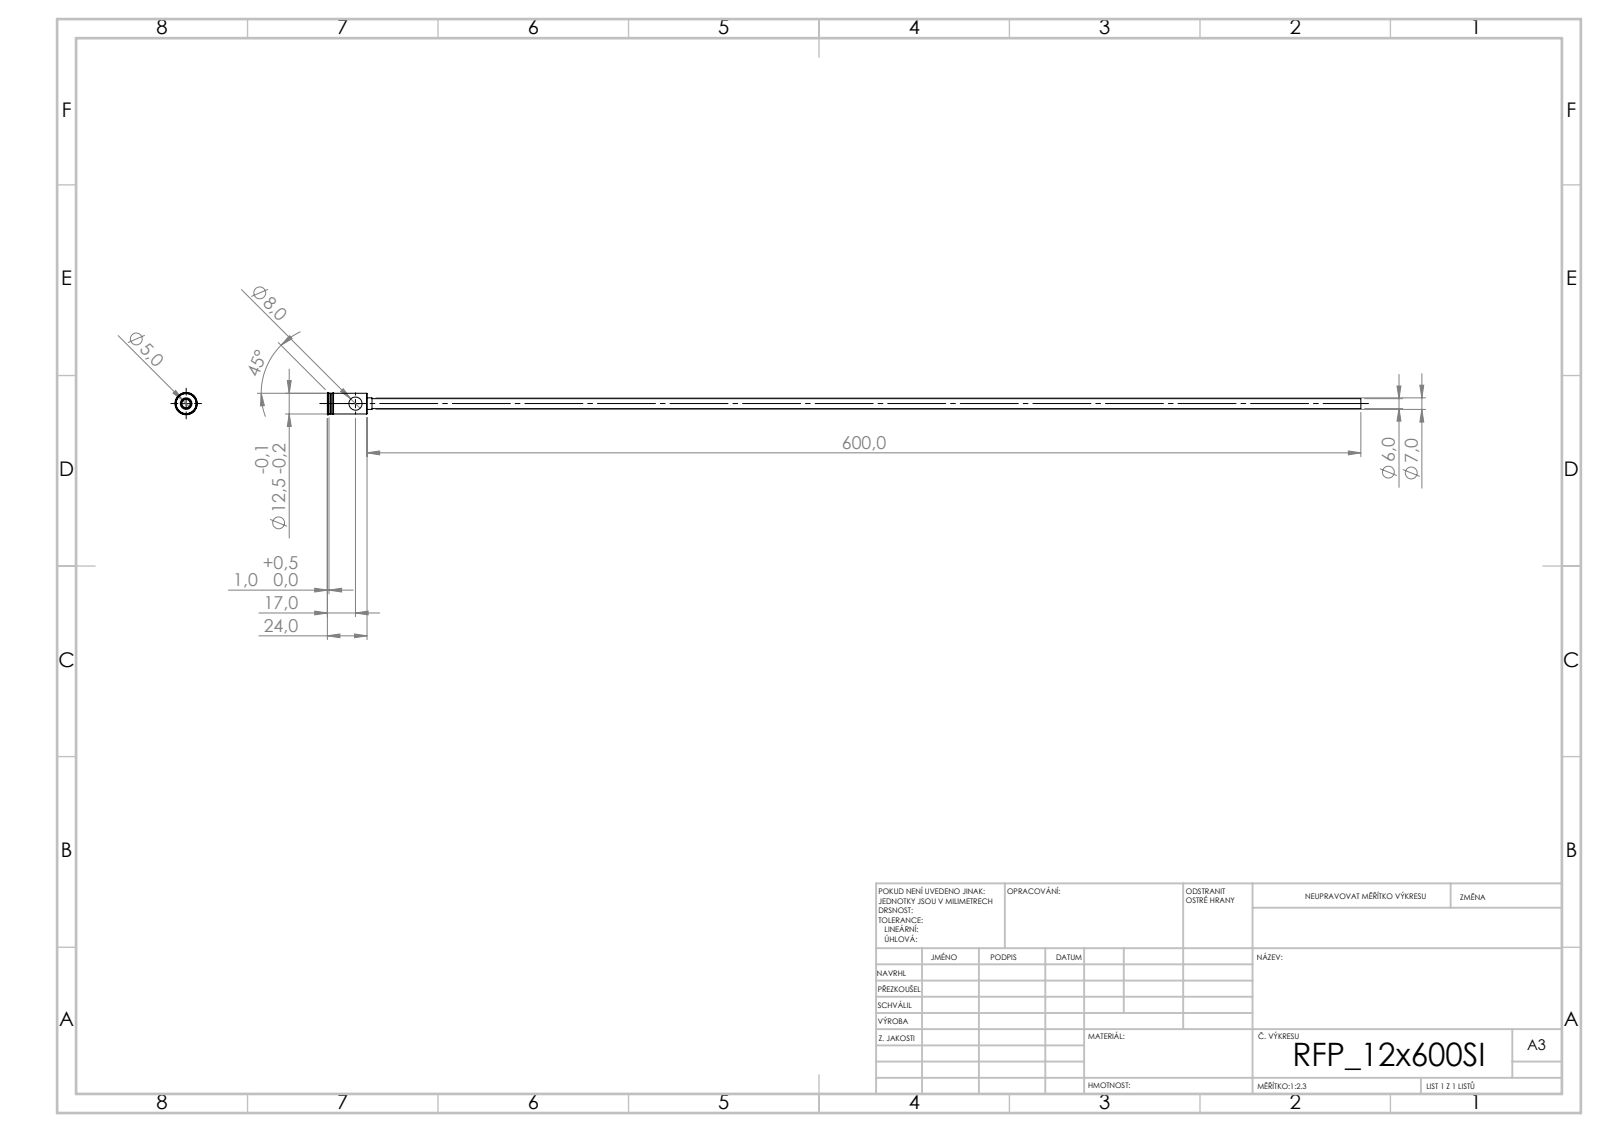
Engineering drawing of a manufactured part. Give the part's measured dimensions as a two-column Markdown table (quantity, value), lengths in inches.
| quantity | value |
| --- | --- |
| STEP written by | SolidWorks 2019 (CONFIG_CONTROL_DESIGN) |
| units | inches |
| bodies | 1 solid, 44 faces (20 planar, 16 cylindrical, 8 other) |
| overall size | 24.567 × 0.531 × 0.531 |
| volume | 0.452 in³ |
| surface area | 34.45 in² |
| round holes (diameter × count) | 0.197 × 1, 0.315 × 1 |
| round bosses / shafts (diameter × count) | 0.531 × 1, 0.492 × 1, 0.276 × 1, 0.236 × 1 |
| main face-to-face distances | 0.945, 0.866, 0.079, 0.311, 0.854, 0.091, 0.118, 0.972, 0.984, 1.063 |
